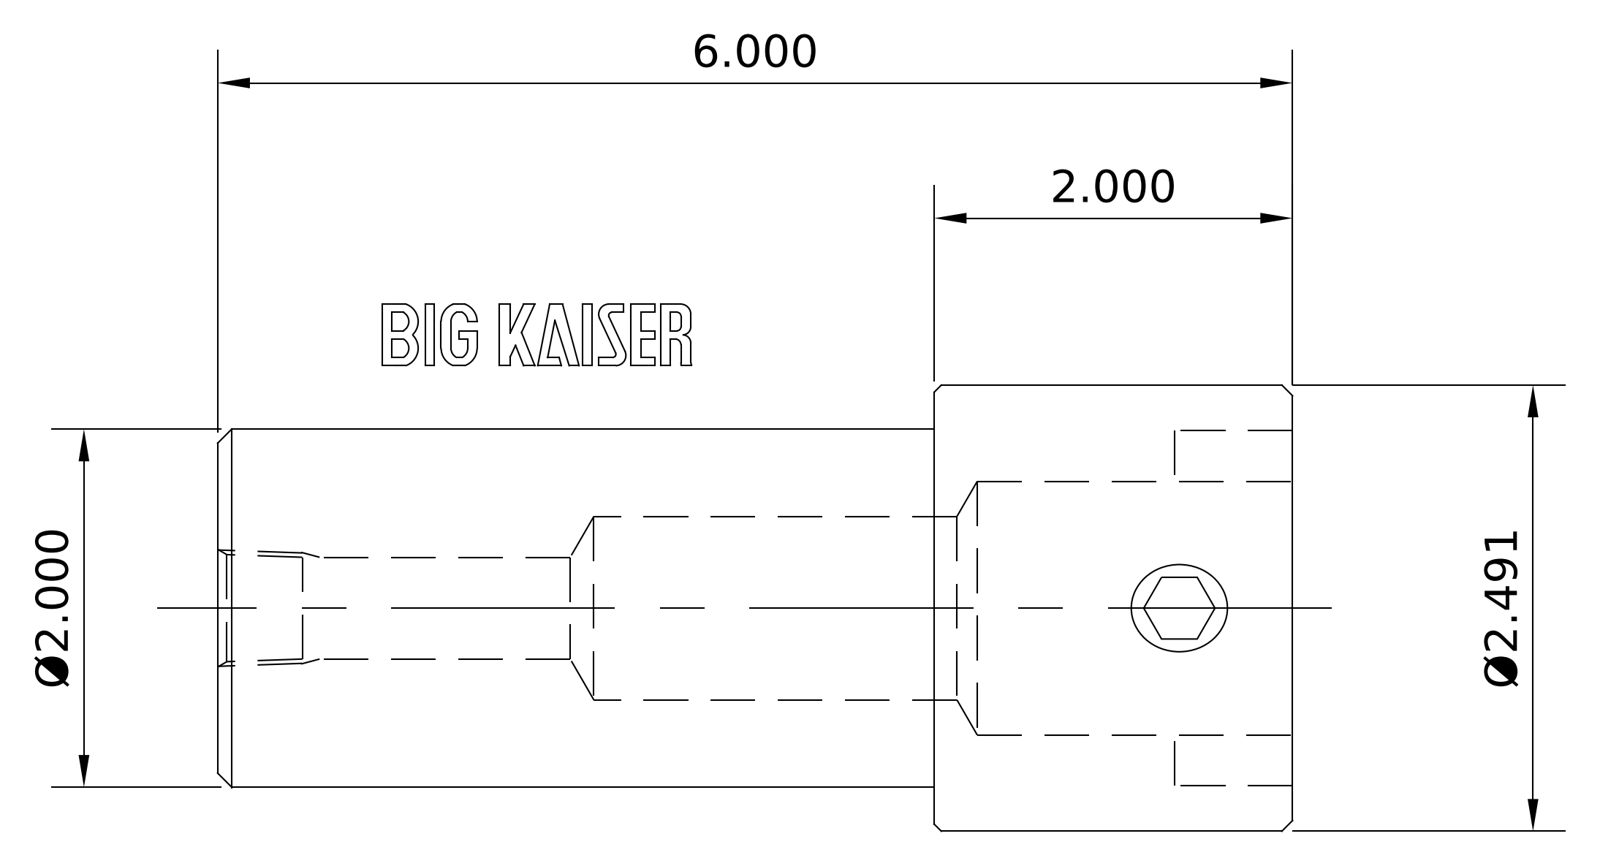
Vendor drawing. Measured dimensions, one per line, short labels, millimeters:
name: 11.361.462
written by: SolidWorks 2018 (CONFIG_CONTROL_DESIGN)
unit: mm
bodies: 1 solid, 63 faces (22 planar, 15 cylindrical, 26 other)
size: 154.2 × 63.27 × 63.27
volume: 280 727 mm³; area: 43 469 mm²
holes: 1× ⌀10.2, 1× ⌀11.13, 1× ⌀14.27, 1× ⌀26, 1× ⌀33, 1× ⌀36
bosses: 1× ⌀63.27, 1× ⌀50.79, 1× ⌀36.5
rounds: 2× R5.5, 1× R6.15
face distances: 154.2, 109.2, 45, 30.7, 6.91, 103.4, 5.8, 50.8, 137.6, 34.2
hole spacings: 25.15
